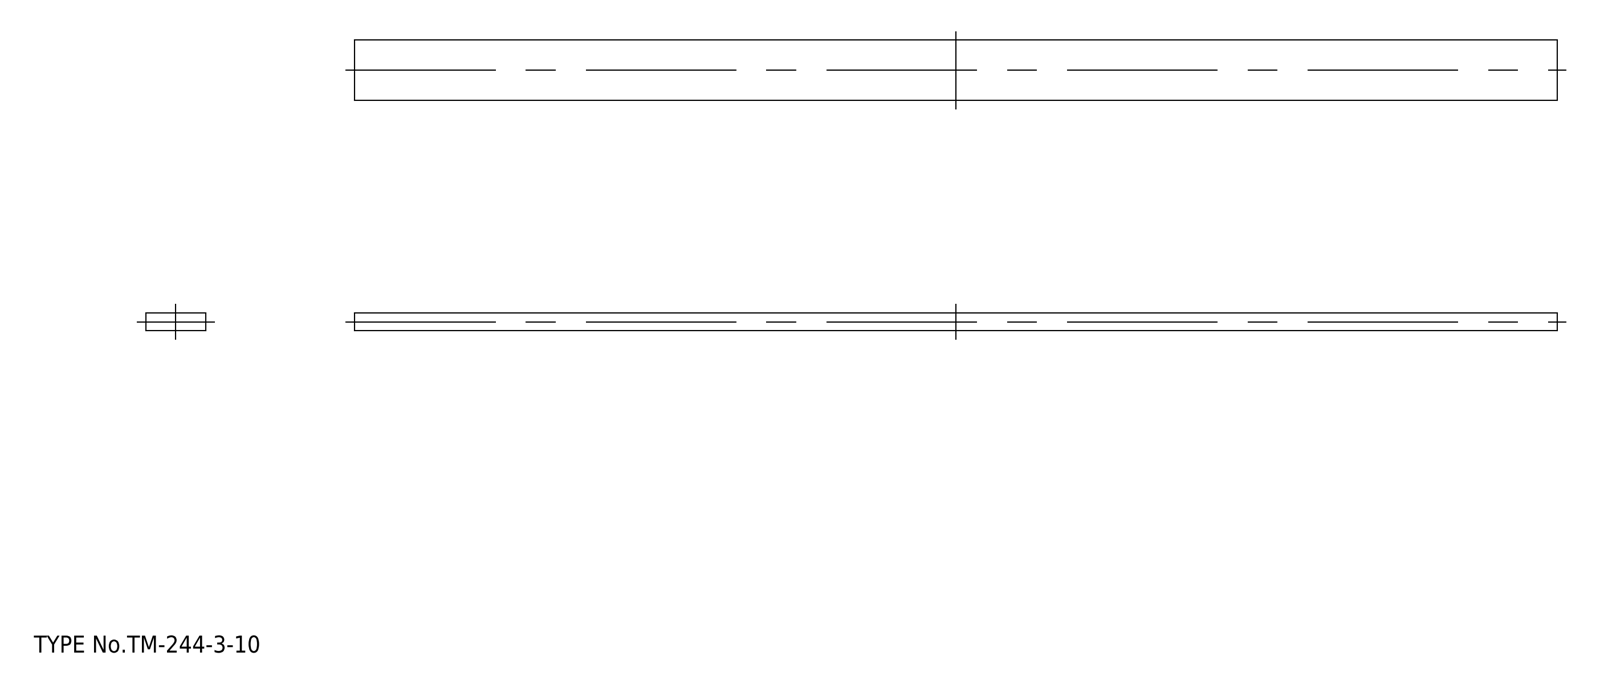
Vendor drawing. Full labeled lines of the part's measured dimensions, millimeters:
STEP written by: spGate 18.9.1 (****-****-****-****) (AUTOMOTIVE_DESIGN)
Units: millimetres
Bodies: 1 solid, 6 faces (6 planar, 0 cylindrical, 0 other)
Overall size (bounding box): 200 × 10 × 3
Volume: 6 000 mm³ · Surface area: 5 260 mm²
Main face-to-face distances: 3, 10, 200
